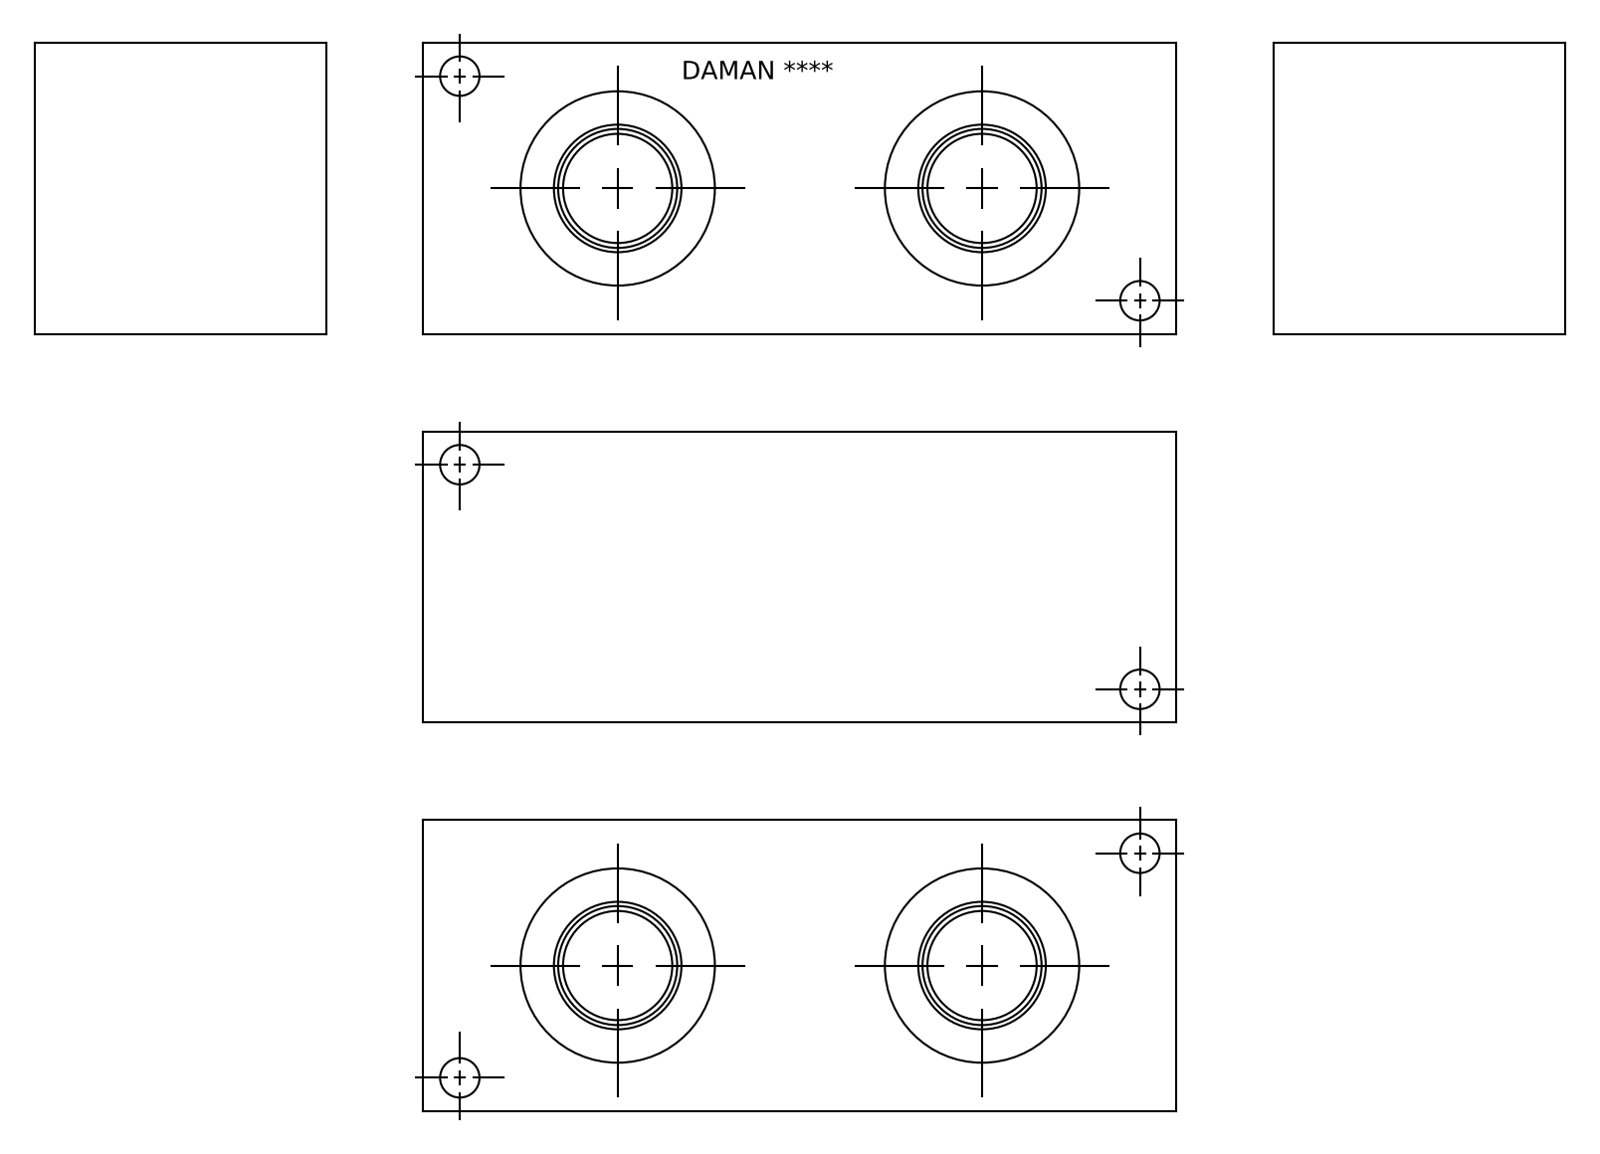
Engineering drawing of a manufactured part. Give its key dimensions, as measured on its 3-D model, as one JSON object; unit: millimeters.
{"part_name": "Part_+J1800216S_3D", "step_written_by": "Autodesk Inventor 2020 (AUTOMOTIVE_DESIGN)", "units": "millimeters", "bodies": {"solids": 1, "faces": 380, "planar": 223, "cylindrical": 31, "other": 126}, "overall_size": [196.85, 76.2, 76.2], "volume_mm3": 1003000, "surface_area_mm2": 92511, "round_holes": [[10.31, 4], [28.57, 2], [31.27, 2], [33.35, 2], [33.76, 2], [35.51, 2], [49.12, 2], [33.34, 1]], "face_to_face_distances": [76.2, 196.85, 0.79, 75.41, 74.62, 19.84, 56.36, 19.05, 55.57, 36.52], "hole_center_spacings": [50.65, 139.64, 187.24, 95.25]}
